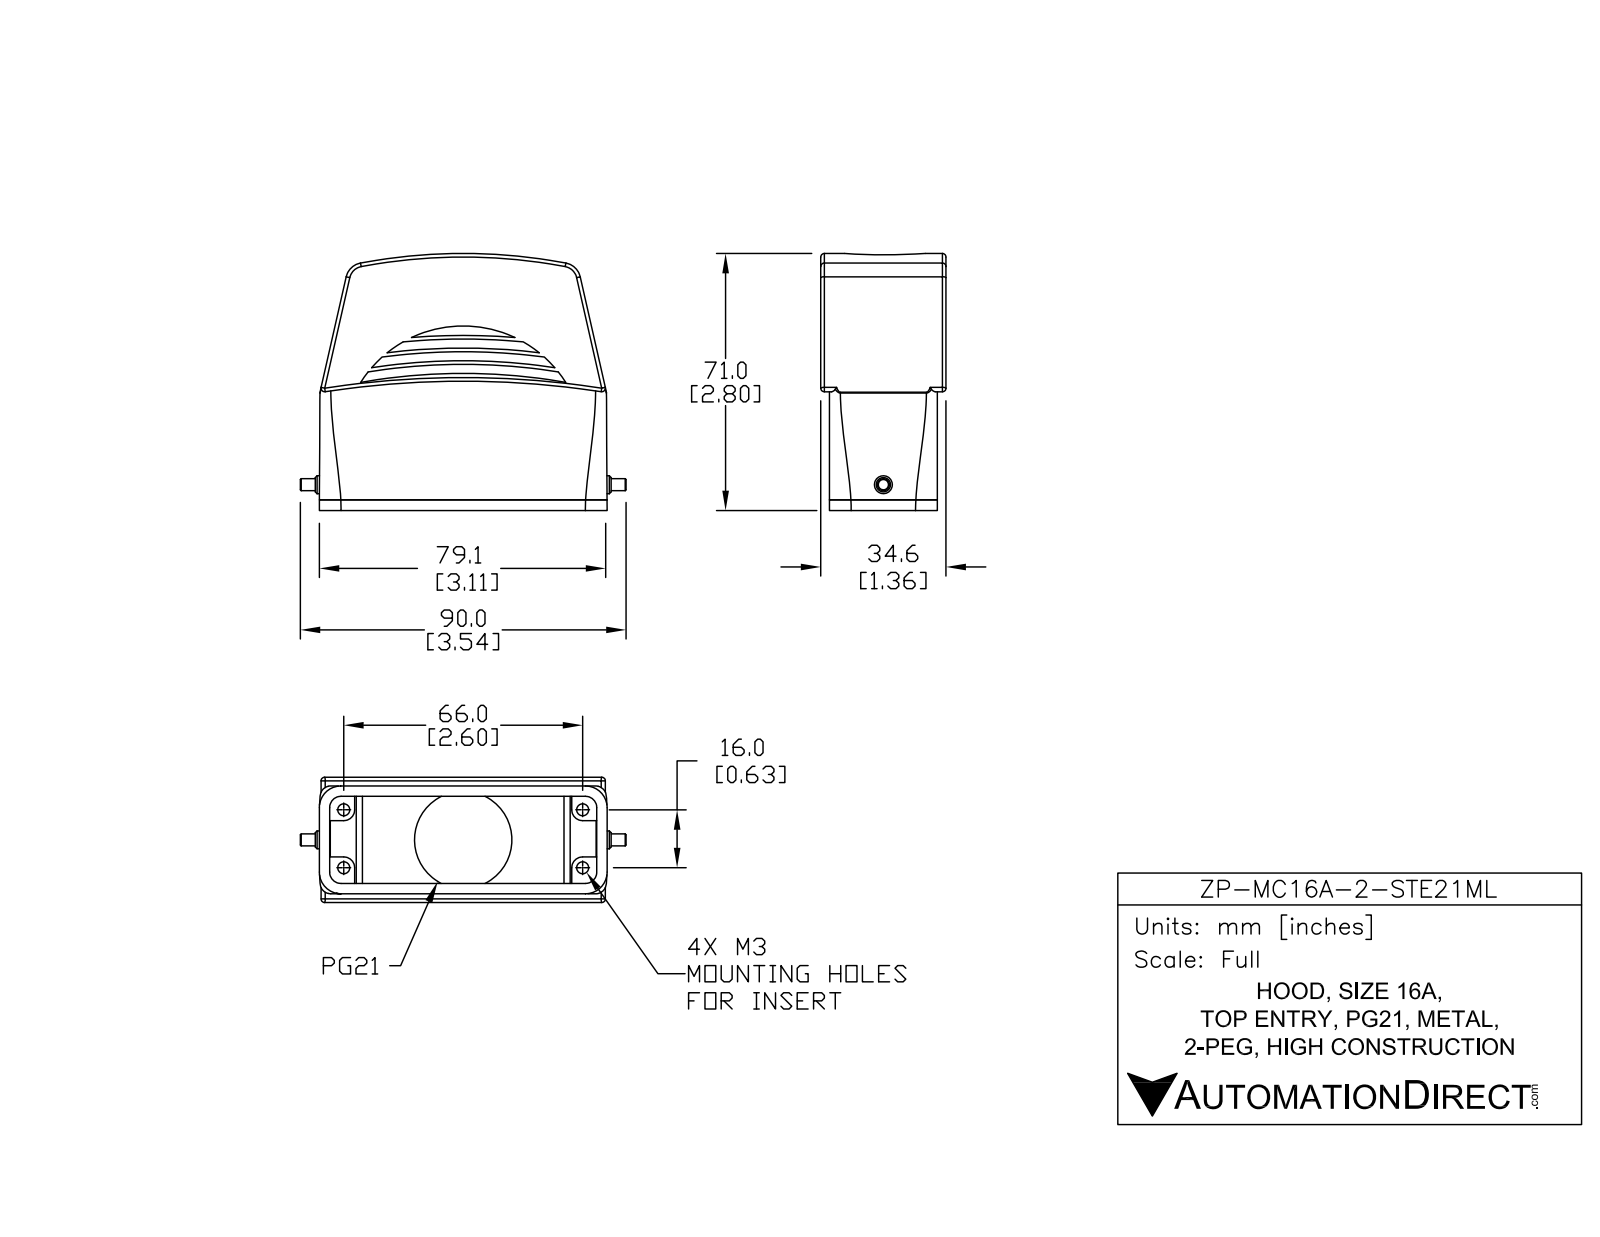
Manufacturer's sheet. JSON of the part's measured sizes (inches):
{"part_name": "ZP-MC16A-2-STE21ML", "step_written_by": "SolidWorks 2014 (AUTOMOTIVE_DESIGN)", "units": "inches", "bodies": {"solids": 2, "faces": 227, "planar": 56, "cylindrical": 97, "other": 74}, "overall_size": [3.543, 2.795, 1.362], "volume_in3": 3.586, "surface_area_in2": 50.64, "round_holes": [[0.13, 4], [1.063, 1]], "round_bosses_or_shafts": [[0.195, 1], [0.131, 1]], "partial_cylinders_radius": [[0.039, 9], [0.118, 4], [0.085, 2], [0.197, 2], [1.321, 1], [5.929, 1], [6.041, 1], [6.478, 1]], "face_to_face_distances": [0.112, 1.06, 0.095, 0.207, 1.155, 1.267, 0.948, 1.172, 1.362, 1.352], "hole_center_spacings": [1.351, 0.654, 2.621, 2.702]}
